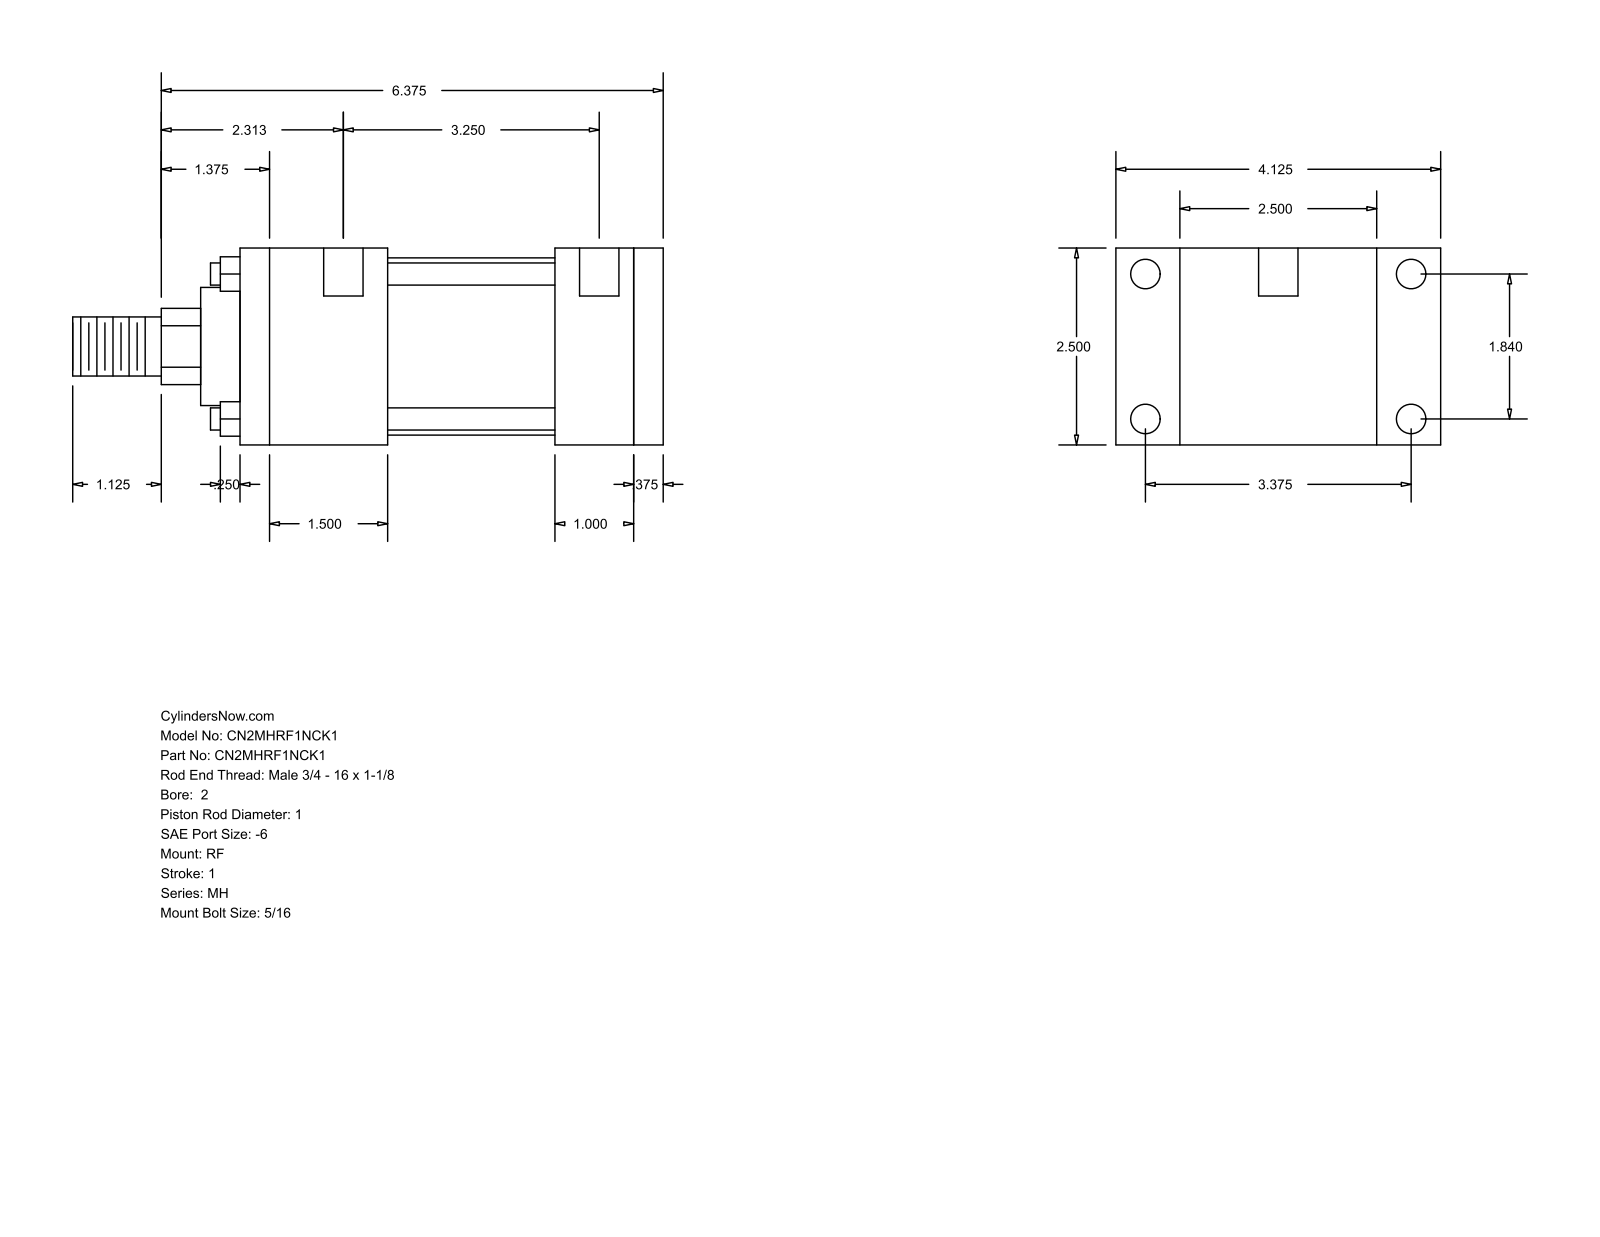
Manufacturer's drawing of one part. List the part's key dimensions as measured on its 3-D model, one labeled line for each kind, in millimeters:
Part name (STEP PRODUCT): MH_RF__0200_1
STEP written by: GSSL Pune (CONFIG_CONTROL_DESIGN)
Units: millimetres
Bodies: 0 solids, 92 faces (64 planar, 28 cylindrical, 0 other)
Overall size (bounding box): 190.5 × 104.78 × 63.5
Round holes (diameter × count): ⌀5.56 ×4, ⌀9.53 ×4, ⌀12.7 ×2
Round bosses / shafts (diameter × count): ⌀7.14 ×4, ⌀57.15 ×1, ⌀38.1 ×1, ⌀25.4 ×1, ⌀19.05 ×1
Partial cylindrical surfaces — rounded edges, fillets, slot ends (radius × count): R12.29 ×1
Main face-to-face distances: 63.5, 136.53, 127, 9.53, 53.97, 101.6, 20.64, 25.4, 47.63, 79.37
Hole centre spacings: 85.72, 46.74, 90.48, 97.63, 3.17, 4.76, 82.55, 87.31
